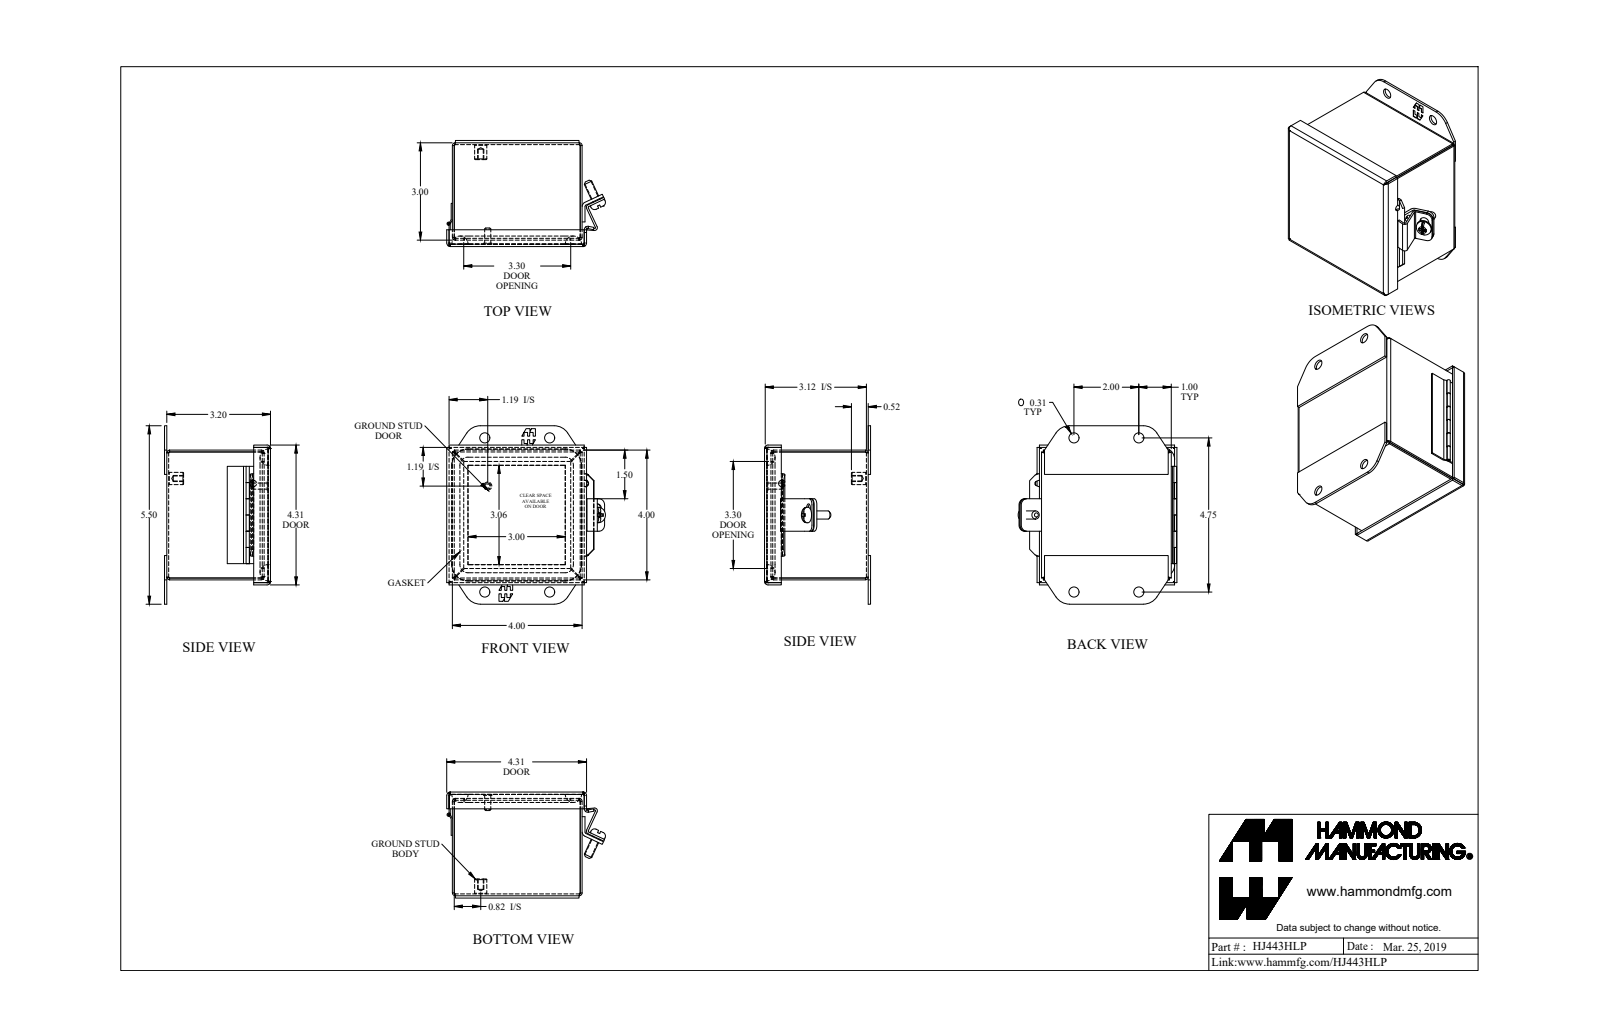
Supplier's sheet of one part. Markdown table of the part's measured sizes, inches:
| quantity | value |
| --- | --- |
| part name | HJ443HLP |
| STEP written by | SolidWorks 2018 (AUTOMOTIVE_DESIGN) |
| units | inches |
| bodies | 13 solids, 490 faces (283 planar, 129 cylindrical, 78 other) |
| overall size | 5.5 × 4.896 × 3.269 |
| volume | 8.126 in³ |
| surface area | 258.2 in² |
| round holes (diameter × count) | 0.313 × 4, 0.05 × 1, 0.156 × 1, 0.213 × 1 |
| round bosses / shafts (diameter × count) | 0.25 × 2, 0.48 × 1, 0.375 × 1, 0.188 × 1, 0.1 × 1, 0.045 × 1 |
| partial cylindrical surfaces (radius × count) | 0.188 × 14, 0.029 × 10, 0.086 × 10, 0.036 × 5, 0.108 × 5, 0.25 × 4, 0.499 × 4, 0.5 × 4 |
| main face-to-face distances | 0.057, 3.943, 0.072, 3.197, 3.125, 4, 3.886, 0.057, 3.068, 3.14 |
| hole center spacings | 2, 4.75, 5.154, 1.257, 2.466, 3.502, 4.094 |
